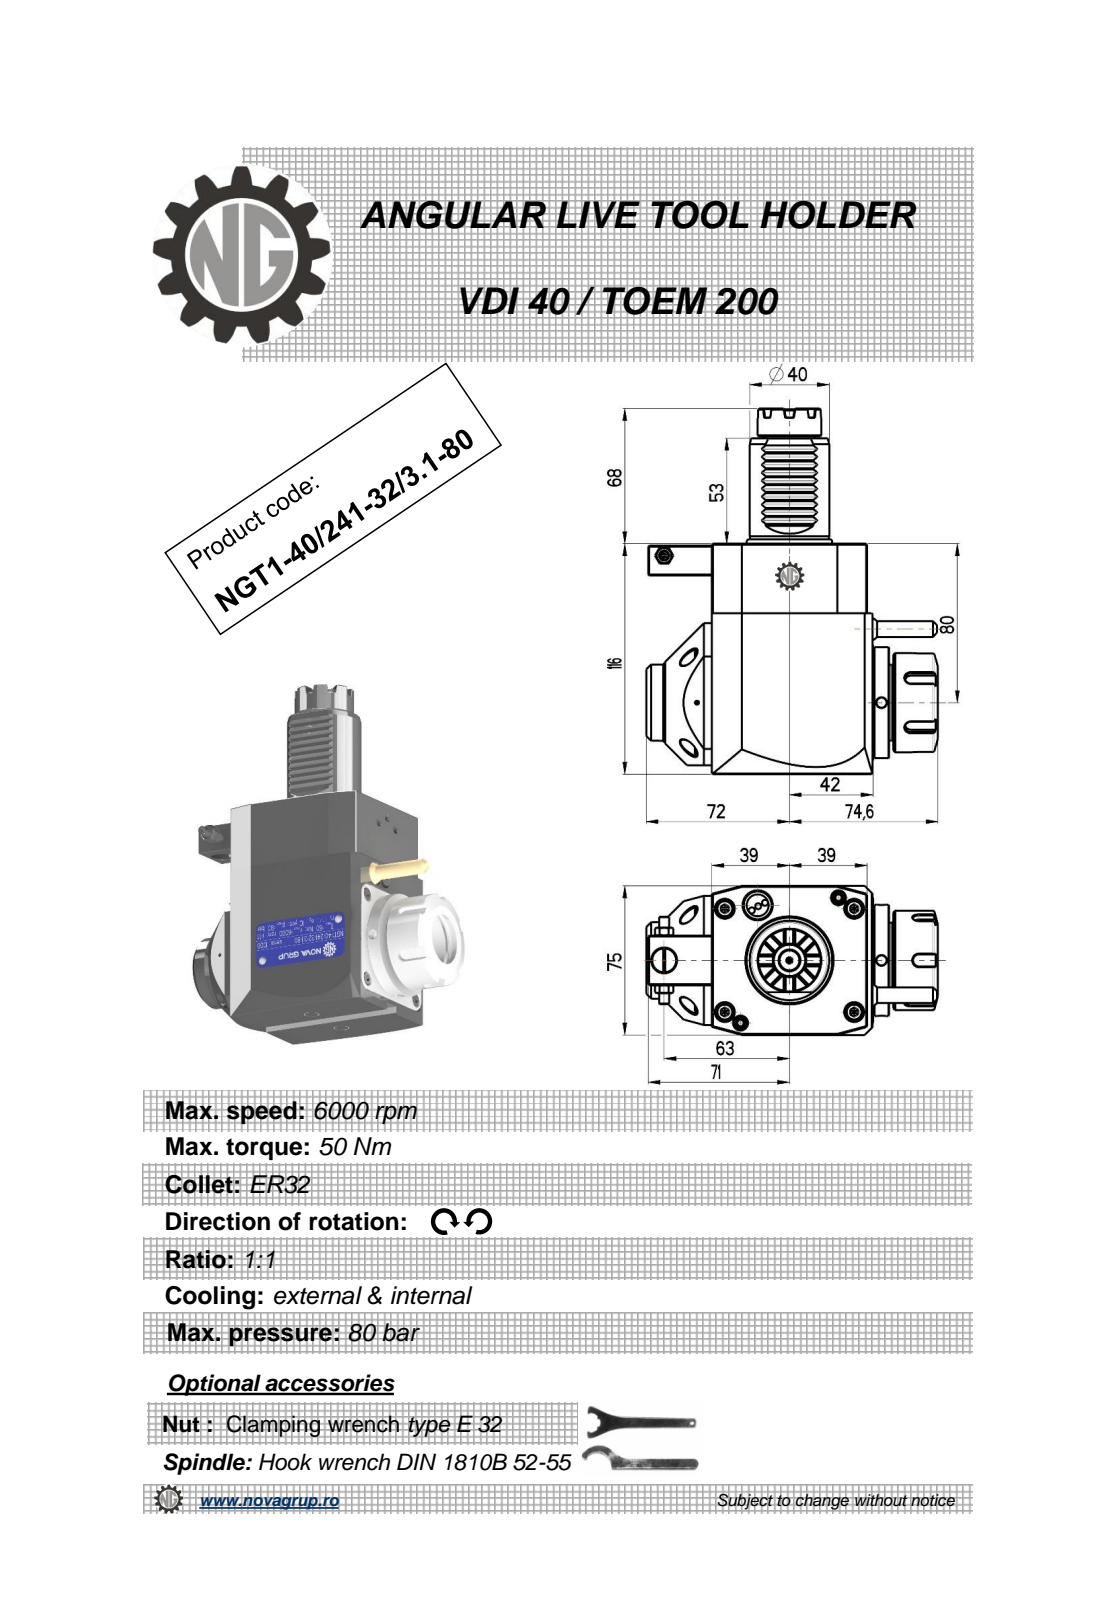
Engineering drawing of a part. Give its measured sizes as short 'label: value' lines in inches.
name: NGT1_40_241_32_3_1_80
written by: PRO/ENGINEER BY PARAMETRIC TECHNOLOGY CORPORATION, 2010280 (CONFIG_CONTROL_DESIGN)
unit: in
bodies: 1 solid, 491 faces (228 planar, 87 cylindrical, 176 other)
size: 7.244 × 5.772 × 2.953
volume: 55.51 in³; area: 114.6 in²
holes: 3× ⌀0.197, 1× ⌀0.118, 1× ⌀0.165, 1× ⌀0.374, 1× ⌀0.472, 1× ⌀1.063
bosses: 1× ⌀2.205, 1× ⌀1.969, 1× ⌀1.693, 1× ⌀1.575, 1× ⌀1.516, 1× ⌀1.26, 1× ⌀0.677, 1× ⌀0.394
rounds: 12× R0.01, 10× R0.012, 6× R0.008, 5× R0.118, 1× R0.02, 1× R1.575
face distances: 2.953, 4.567, 3.071, 3.189, 0.118, 4.37, 3.181, 0.11, 0.295, 0.02
hole spacings: 1.558, 1.611, 2.854, 4.301, 5.195
